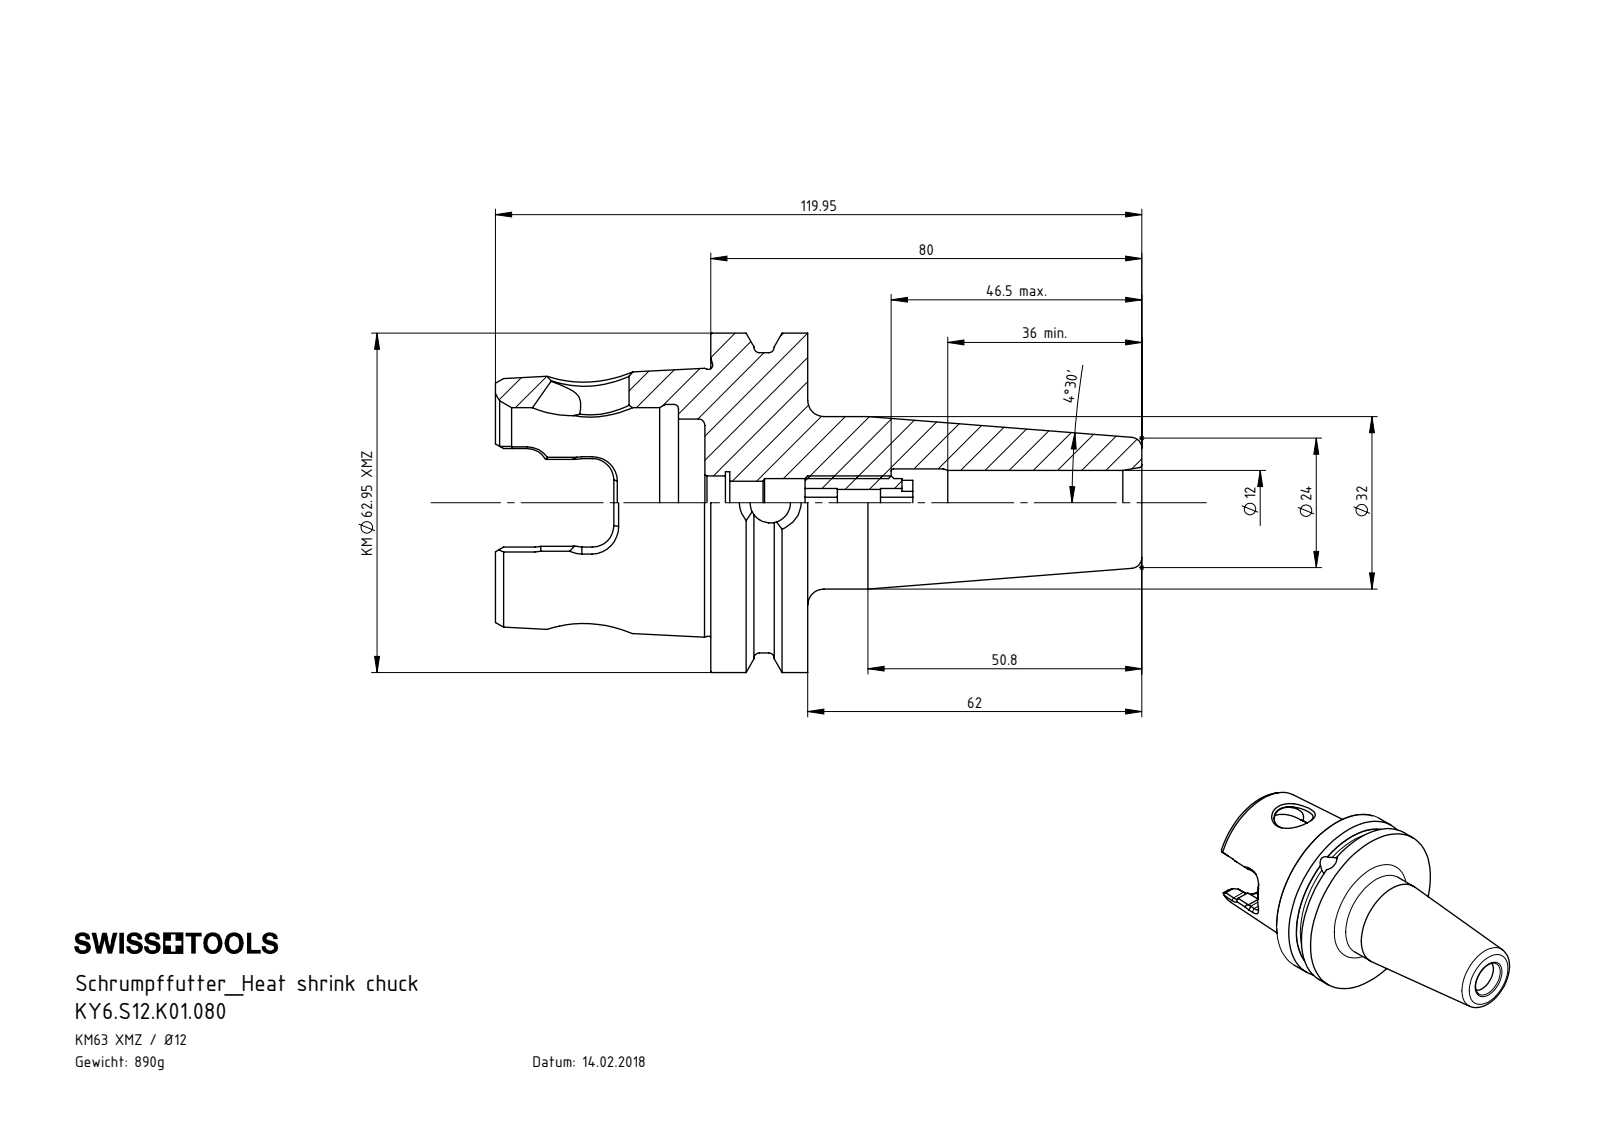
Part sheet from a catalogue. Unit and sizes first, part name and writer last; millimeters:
Units: millimetres
Overall size (bounding box): 119.95 × 62.95 × 62.95
Round holes (diameter × count): ⌀7.47 ×2, ⌀5 ×1, ⌀8 ×1, ⌀8.48 ×1, ⌀9 ×1, ⌀10 ×1, ⌀11.5 ×1, ⌀12 ×1, ⌀12.6 ×1, ⌀14.5 ×1, ⌀31.1 ×1, ⌀35.27 ×1
Round bosses / shafts (diameter × count): ⌀62.95 ×1, ⌀55.7 ×1, ⌀32 ×1
Partial cylindrical surfaces — rounded edges, fillets, slot ends (radius × count): R4 ×6, R7.04 ×2
Main face-to-face distances: 18, 1.1, 19.1, 33.95, 6, 4.9, 24, 38.85, 39.95, 57.95
Volume: 113 398 mm³ · Surface area: 28 490 mm²
Bodies: 2 solids, 272 faces (79 planar, 60 cylindrical, 133 other)
Part name (STEP PRODUCT): KY6-S12.K01.080; ERU-AN4.K01.020_A; KY6-S12.K01.080_A
STEP written by: SolidWorks 2012 (CONFIG_CONTROL_DESIGN)
